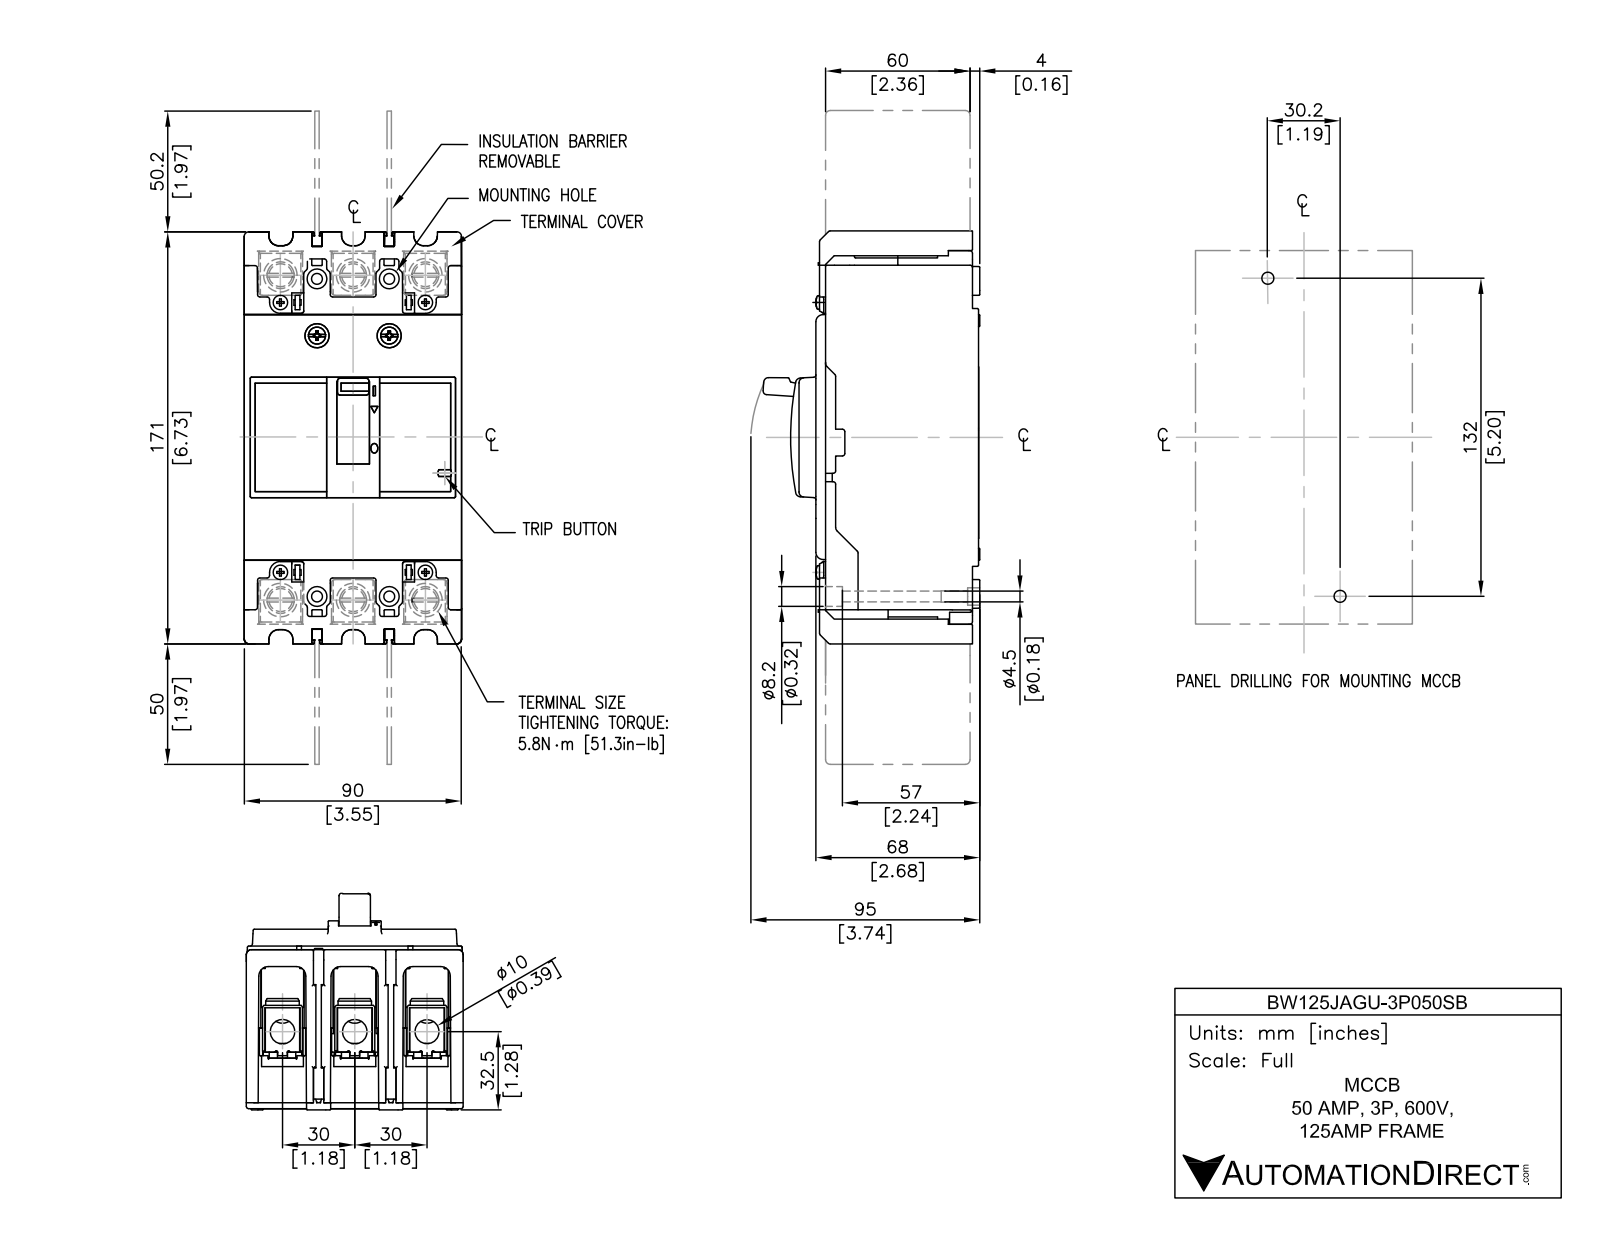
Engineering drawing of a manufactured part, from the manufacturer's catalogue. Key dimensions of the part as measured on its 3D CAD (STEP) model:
Part name (STEP PRODUCT): BW125JAGU-3P050SB
STEP written by: SolidWorks 2018 (AUTOMOTIVE_DESIGN)
Units: inches
Bodies: 14 solids, 452 faces (340 planar, 88 cylindrical, 24 other)
Overall size (bounding box): 10.197 × 3.602 × 3.543
Volume: 57.4 in³ · Surface area: 230.3 in²
Round holes (diameter × count): ⌀0.315 ×6, ⌀0.177 ×4, ⌀0.323 ×4
Round bosses / shafts (diameter × count): ⌀0.472 ×6
Partial cylindrical surfaces — rounded edges, fillets, slot ends (radius × count): R0.157 ×12, R0.079 ×6, R0.118 ×6
Main face-to-face distances: 1.181, 1.11, 1.252, 2.291, 2.433, 0.142, 3.543, 0.236, 2.402, 1.039
Hole centre spacings: 0.593, 5.289, 1.181, 1.772, 5.444, 5.546, 5.315, 2.362
